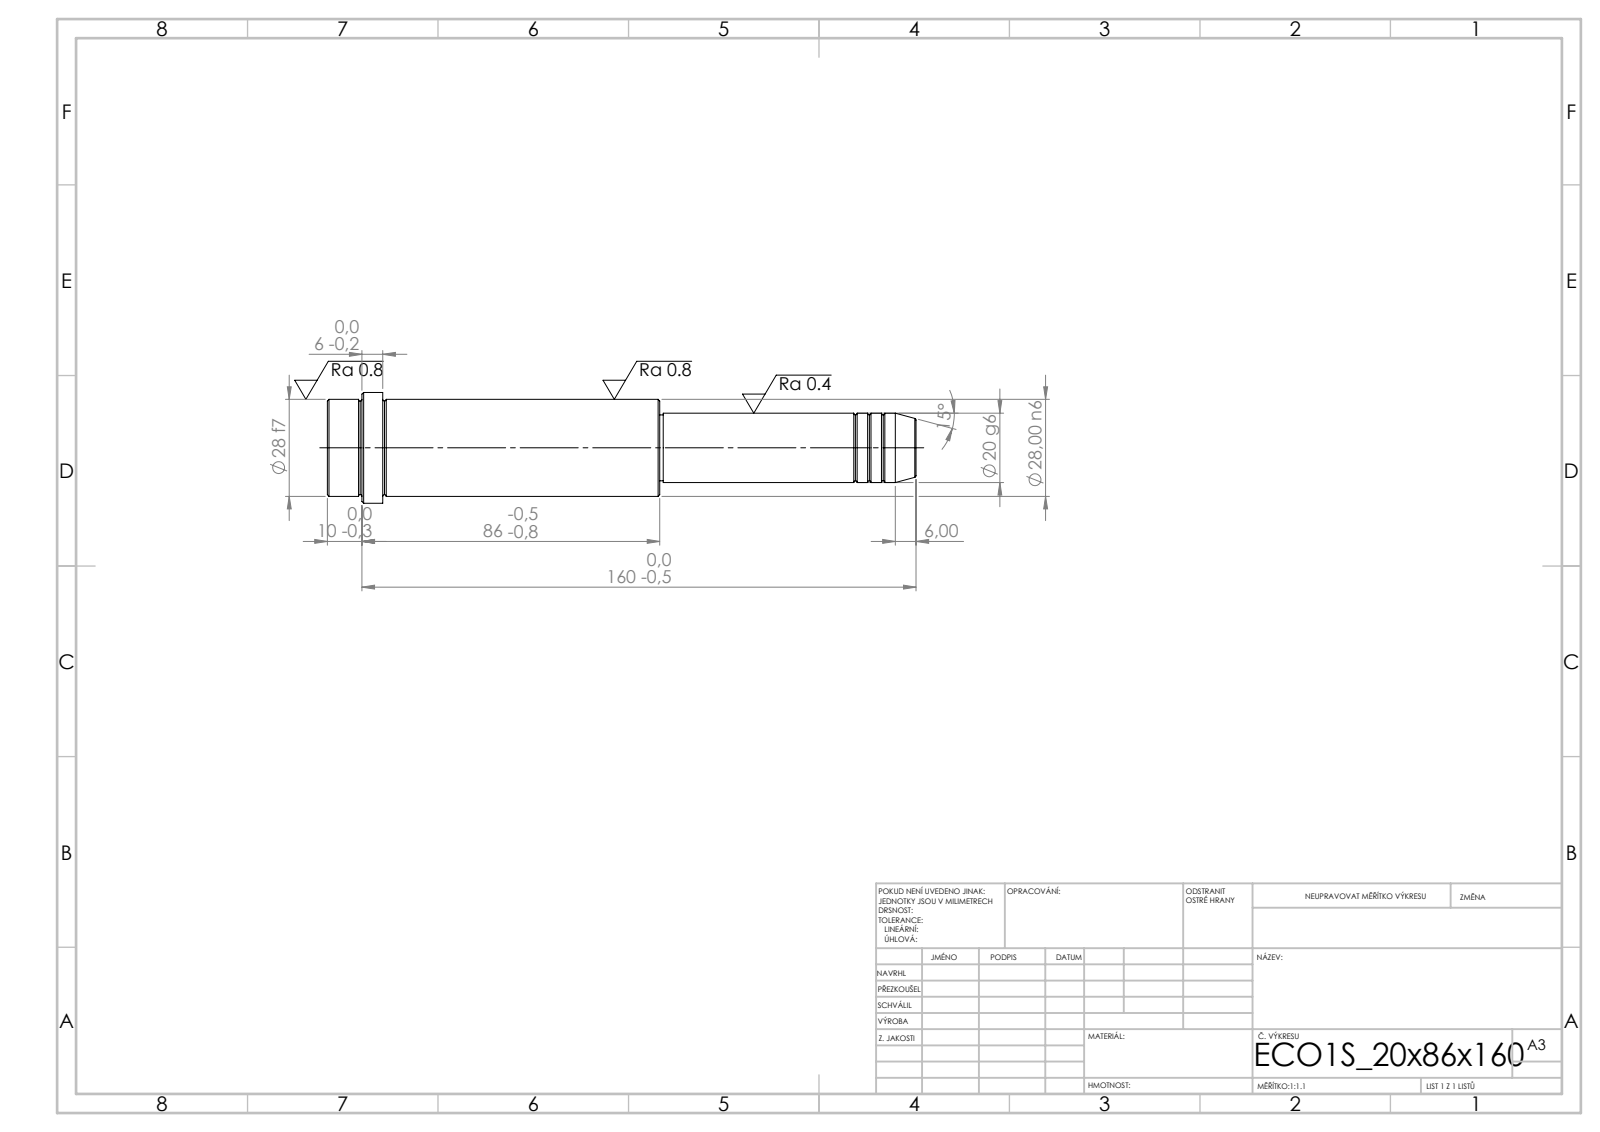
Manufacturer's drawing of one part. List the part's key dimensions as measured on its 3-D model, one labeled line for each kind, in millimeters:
STEP written by: SolidWorks 2019 (CONFIG_CONTROL_DESIGN)
Units: millimetres
Bodies: 1 solid, 52 faces (6 planar, 16 cylindrical, 30 other)
Overall size (bounding box): 170 × 32 × 32
Volume: 82 997 mm³ · Surface area: 14 830 mm²
Round bosses / shafts (diameter × count): ⌀32 ×1, ⌀28 ×1, ⌀20 ×1, ⌀19 ×1
Main face-to-face distances: 96, 74, 170, 154, 80, 16, 160, 86, 6, 10
